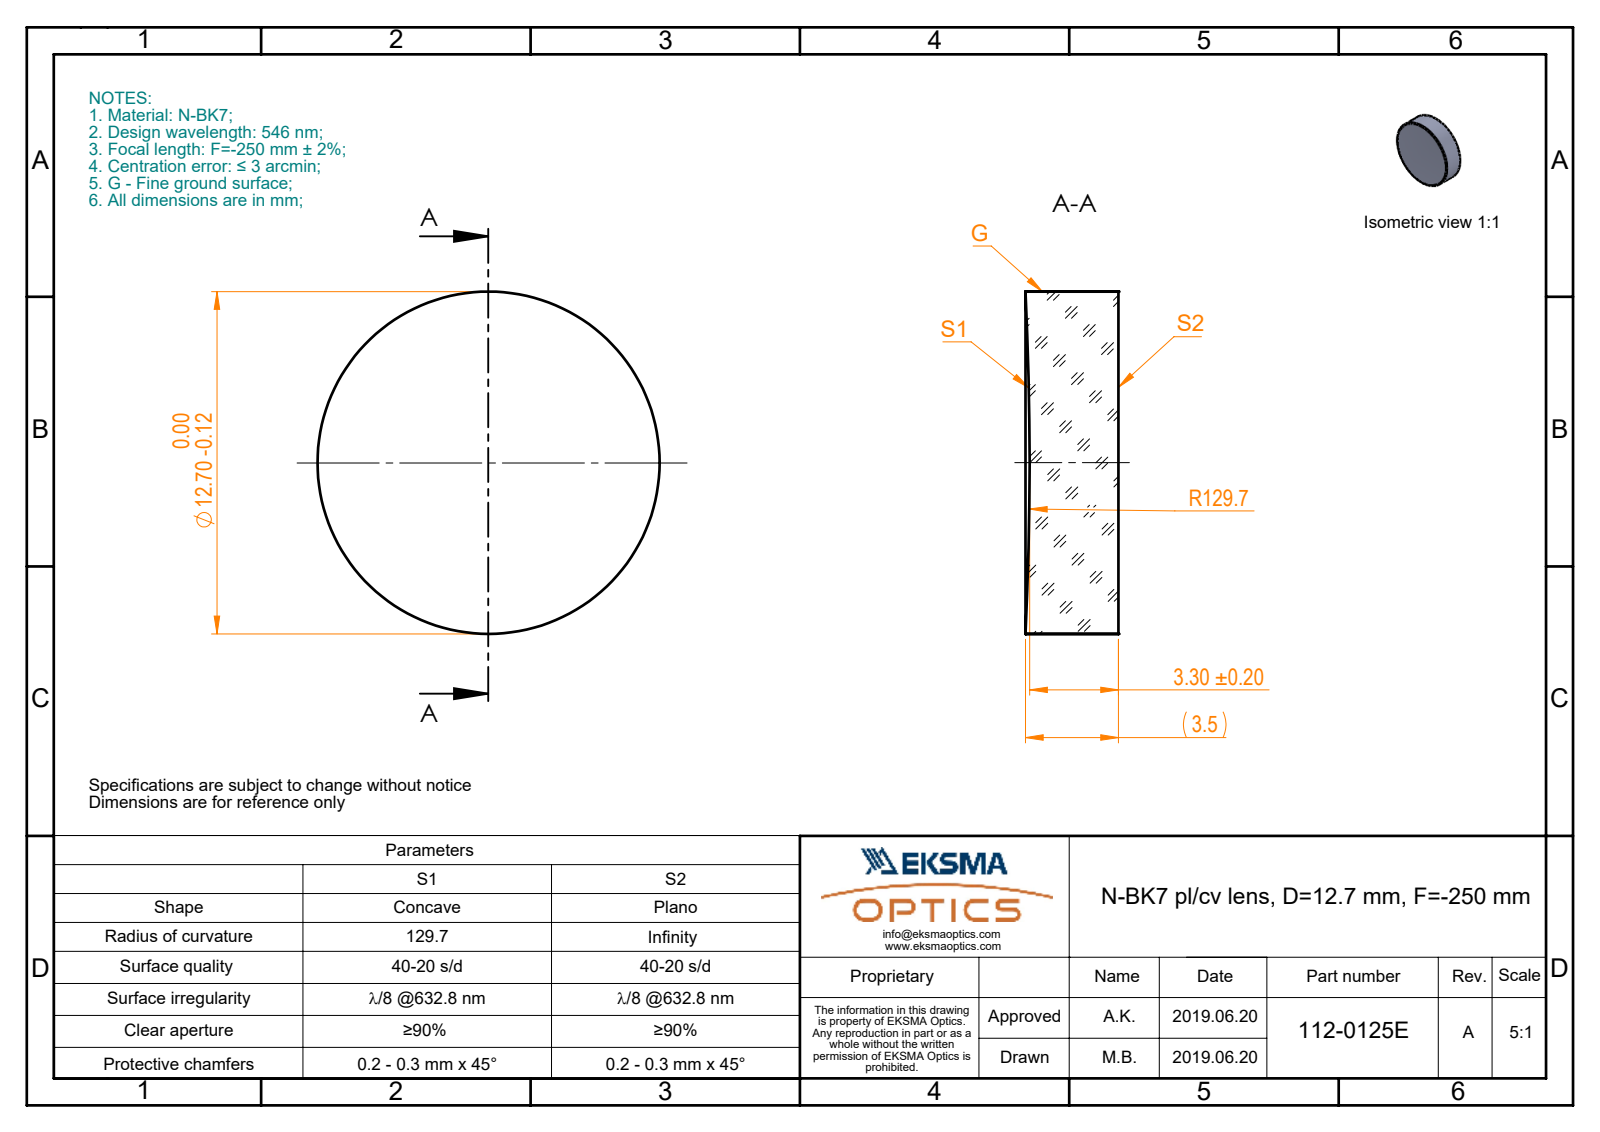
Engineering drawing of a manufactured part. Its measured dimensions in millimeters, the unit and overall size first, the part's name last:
Units: millimetres
Overall size (bounding box): 12.7 × 12.7 × 3.46
Round bosses / shafts (diameter × count): ⌀12.7 ×1
Volume: 428 mm³ · Surface area: 391 mm²
Bodies: 1 solid, 5 faces (1 planar, 2 cylindrical, 2 other)
Part name (STEP PRODUCT): 112-0125E BK7 pl-cv 12.7 F-250
STEP written by: SolidWorks 2017 (AUTOMOTIVE_DESIGN)
